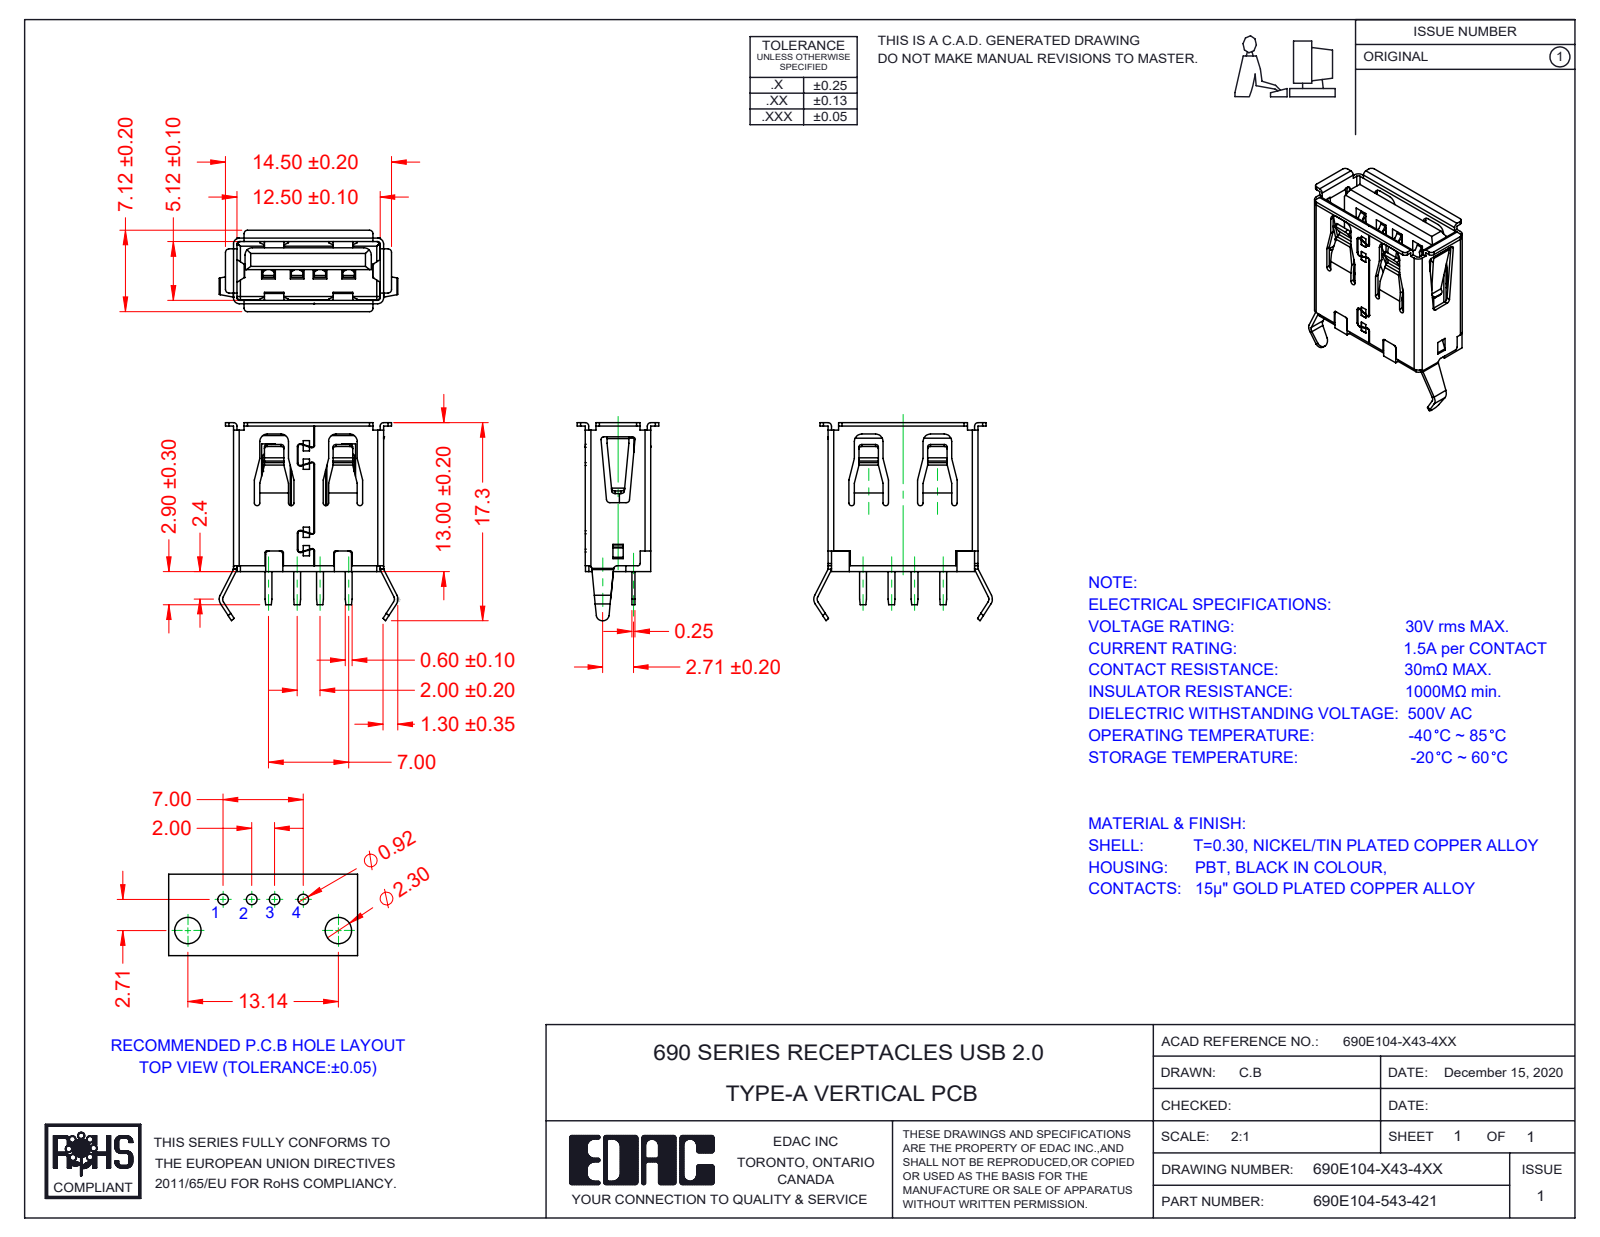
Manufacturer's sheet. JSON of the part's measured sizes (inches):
{"part_name": "Insulator 690E104-X43-4XX_Black; Contacts 690E104-X43-4XX; 690E104-143-421; Shell 690E104-X43-4XX", "step_written_by": "SolidWorks 2020 (AUTOMOTIVE_DESIGN)", "units": "inches", "bodies": {"solids": 6, "faces": 690, "planar": 491, "cylindrical": 194, "other": 5}, "overall_size": [0.681, 0.614, 0.28], "volume_in3": 0.028, "surface_area_in2": 2.734, "partial_cylinders_radius": [[0.008, 37], [0.012, 33], [0.006, 17], [0.01, 14], [0.02, 10], [0.009, 4], [0.022, 4], [0.026, 4]], "face_to_face_distances": [0.213, 0.225, 0.202, 0.055, 0.043, 0.159, 0.17, 0.504, 0.022, 0.177]}
